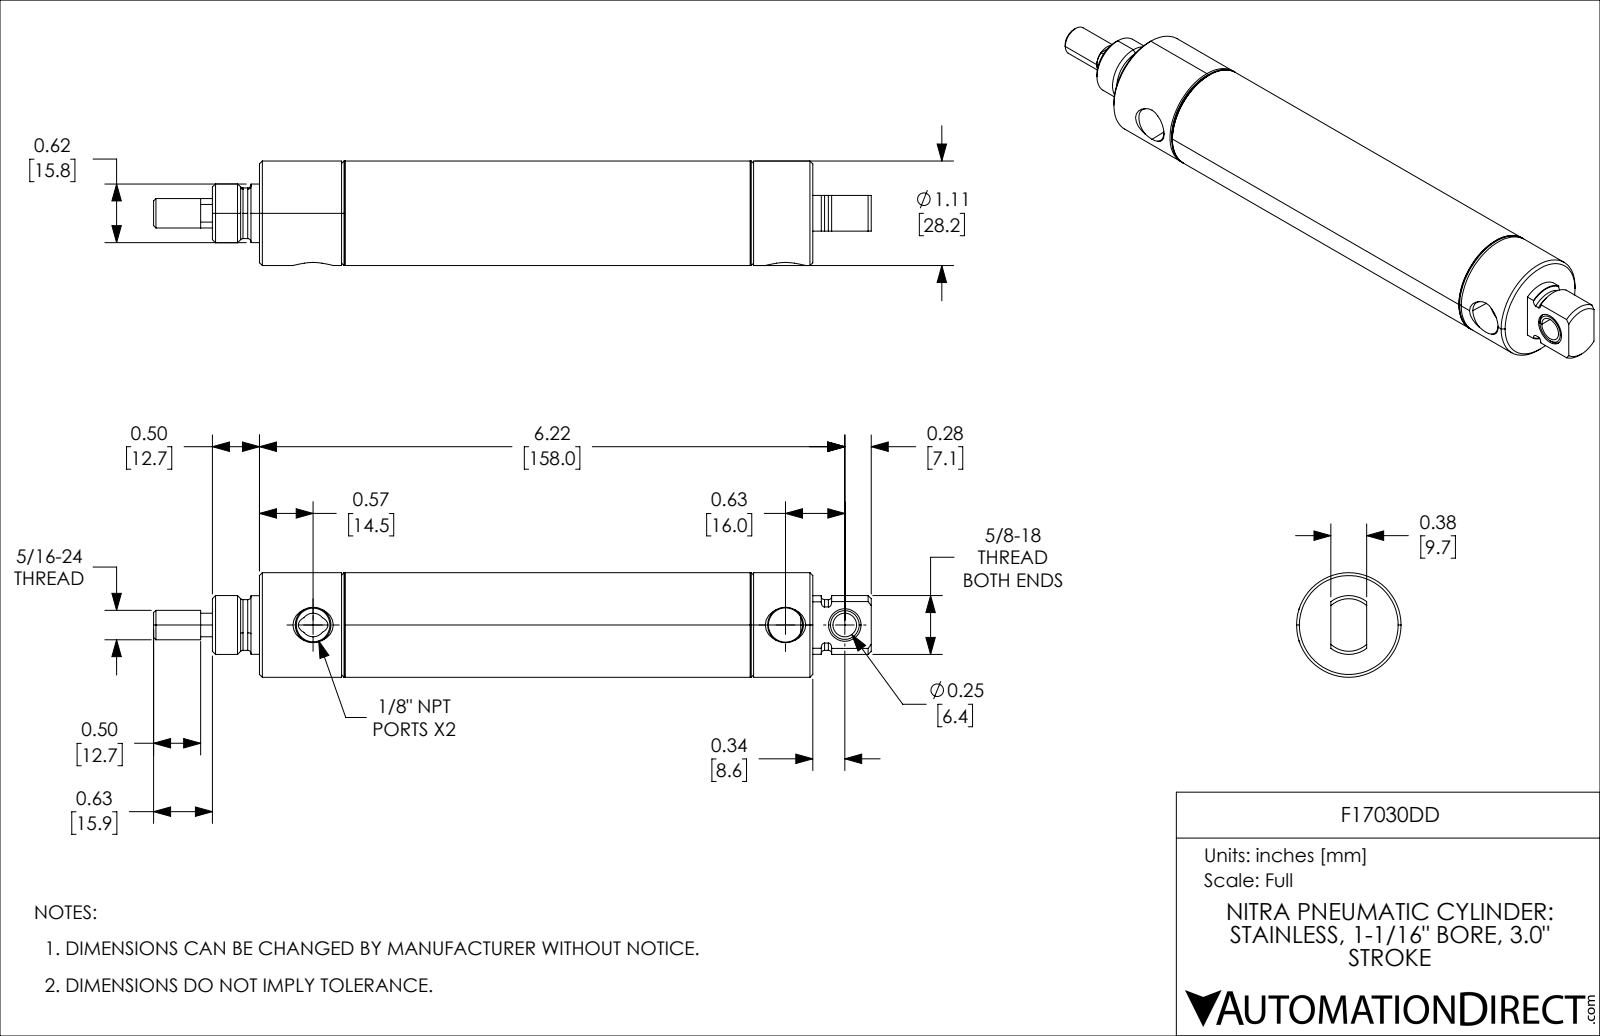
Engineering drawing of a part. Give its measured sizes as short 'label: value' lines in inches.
name: F17030DD_11; F17030DD_3; F17030DD_9; F17030DD_7 (+2 more)
written by: SolidWorks 2021 (CONFIG_CONTROL_DESIGN)
unit: in
bodies: 5 solids, 156 faces (30 planar, 58 cylindrical, 68 other)
size: 7.625 × 1.11 × 1.11
volume: 3.223 in³; area: 57.82 in²
holes: 1× ⌀0.251, 1× ⌀0.336, 1× ⌀0.346, 1× ⌀0.364, 1× ⌀0.375, 1× ⌀0.75, 1× ⌀1.012
bosses: 1× ⌀1.11, 1× ⌀1.072, 1× ⌀0.625, 1× ⌀0.622, 1× ⌀0.539, 1× ⌀0.313, 1× ⌀0.312
rounds: 1× R0.125, 1× R0.269
face distances: 0.875, 3, 3.875, 4.754, 1.754, 0.879, 1.125, 4.125, 5, 5.879
hole spacings: 0.63
